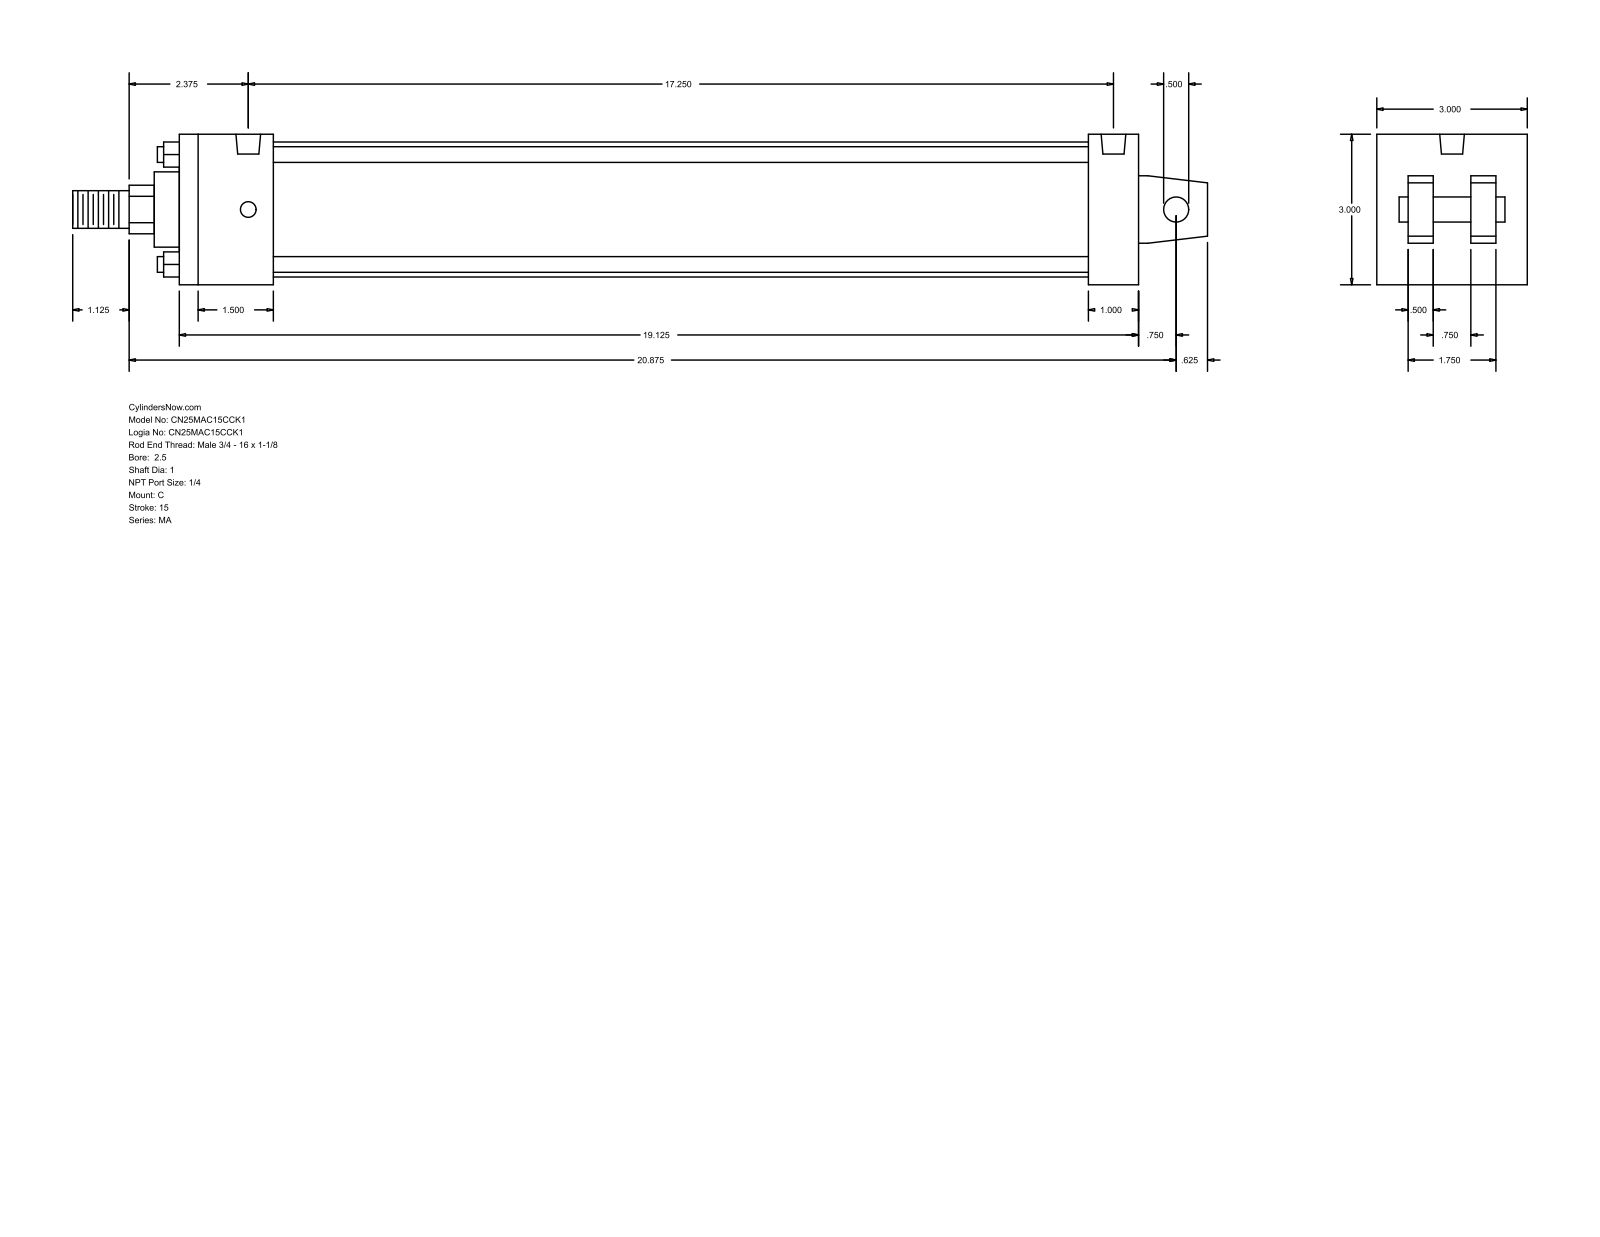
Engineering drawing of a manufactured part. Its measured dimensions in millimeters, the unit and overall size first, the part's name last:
Units: millimetres
Overall size (bounding box): 574.67 × 76.2 × 76.2
Round holes (diameter × count): ⌀7.94 ×4, ⌀12.49 ×2
Round bosses / shafts (diameter × count): ⌀7.94 ×4, ⌀68.33 ×1, ⌀38.1 ×1, ⌀25.4 ×1, ⌀19.05 ×1, ⌀12.7 ×1
Partial cylindrical surfaces — rounded edges, fillets, slot ends (radius × count): R12.29 ×1
Main face-to-face distances: 76.2, 47.63, 485.78, 12.7, 60.33, 15.87, 28.57, 460.37, 412.74, 438.15
Hole centre spacings: 438.15
Bodies: 0 solids, 103 faces (76 planar, 27 cylindrical, 0 other)
Part name (STEP PRODUCT): MA_C__0250_1
STEP written by: GSSL Pune (CONFIG_CONTROL_DESIGN)
